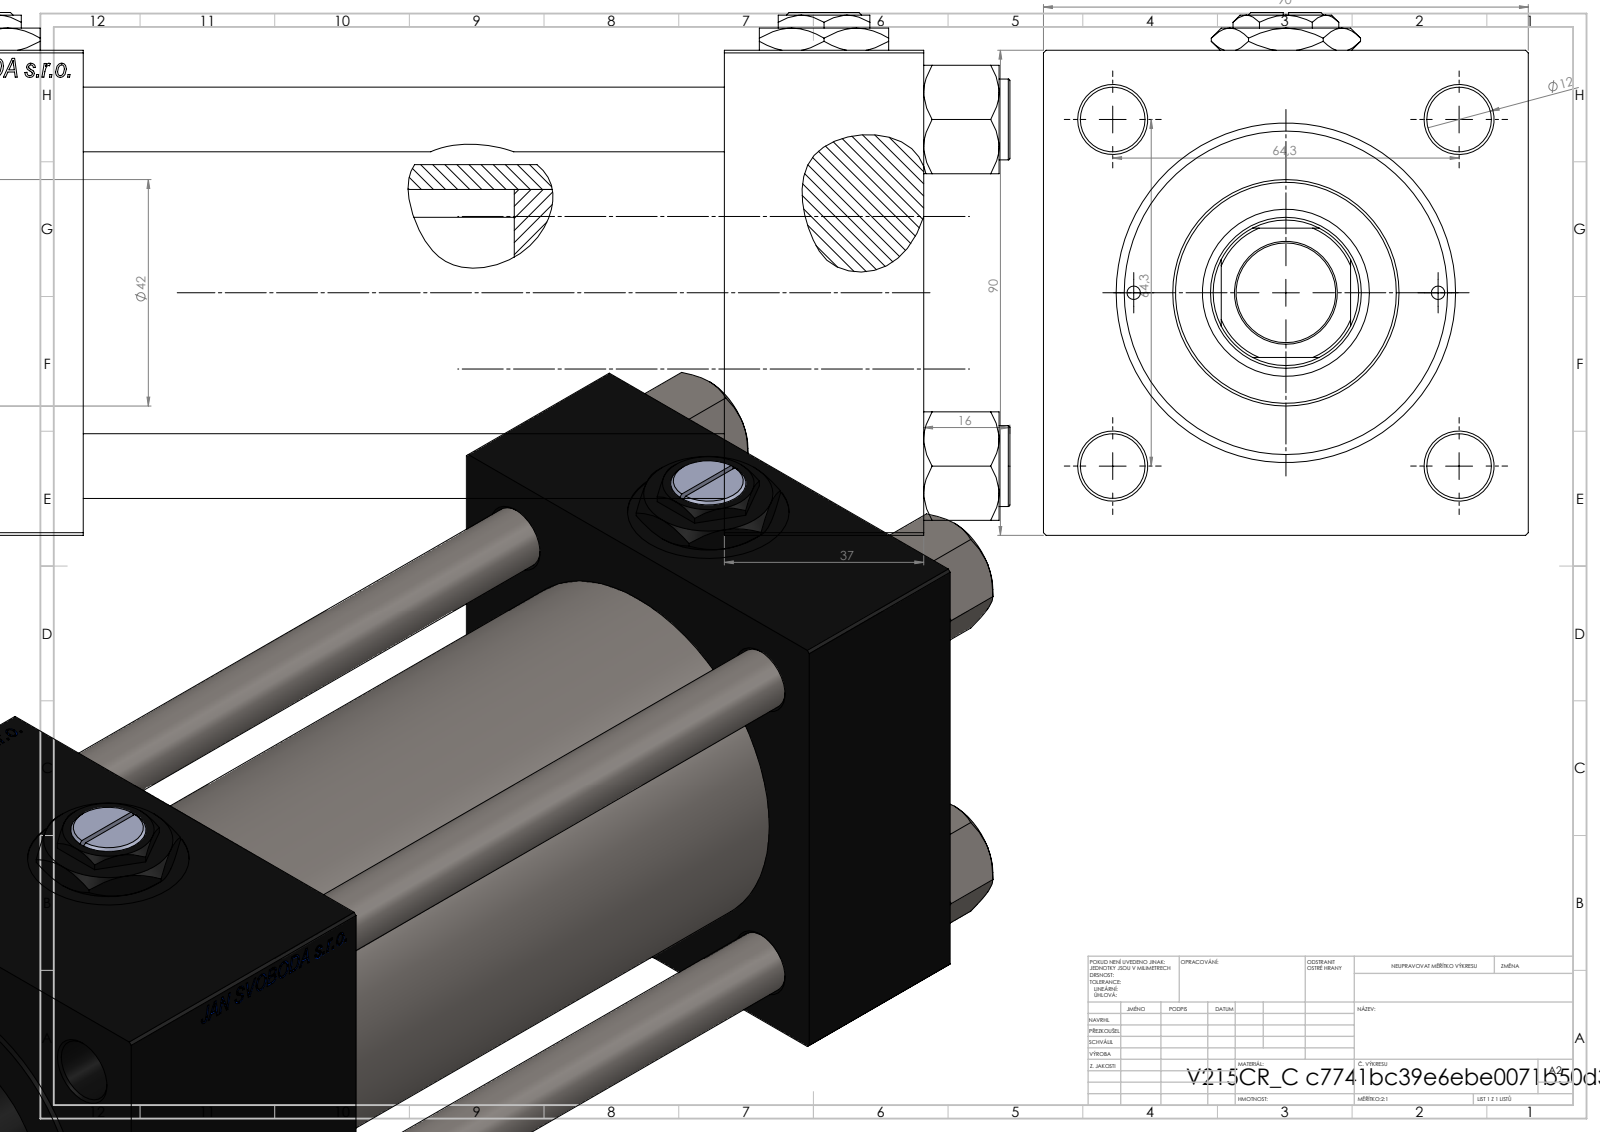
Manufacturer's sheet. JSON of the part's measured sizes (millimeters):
{"part_name": "Zatka_pro_OIL_PORT; V215CR_VCP_C; V215CR_C_TYCINKA; NUT_M5_C (+2 more)", "step_written_by": "SolidWorks 2019 (CONFIG_CONTROL_DESIGN)", "units": "millimeters", "bodies": {"solids": 13, "faces": 1256, "planar": 576, "cylindrical": 102, "other": 578}, "overall_size": [263, 97, 90], "volume_mm3": 1041000, "surface_area_mm2": 223317, "round_holes": [[12, 4], [2.5, 2], [7, 2], [20.96, 2], [30, 2], [18.5, 1], [28, 1], [31, 1], [50, 1], [60, 1], [63, 1]], "round_bosses_or_shafts": [[15, 4], [69, 1], [42, 1]], "partial_cylinders_radius": [[13.5, 1]], "face_to_face_distances": [90, 37, 178, 215, 59, 156, 119, 186.3, 149.3, 30.3], "hole_center_spacings": [32.39, 45.47, 64.3, 68.42, 28.25, 90.93, 56.5, 157.5]}
